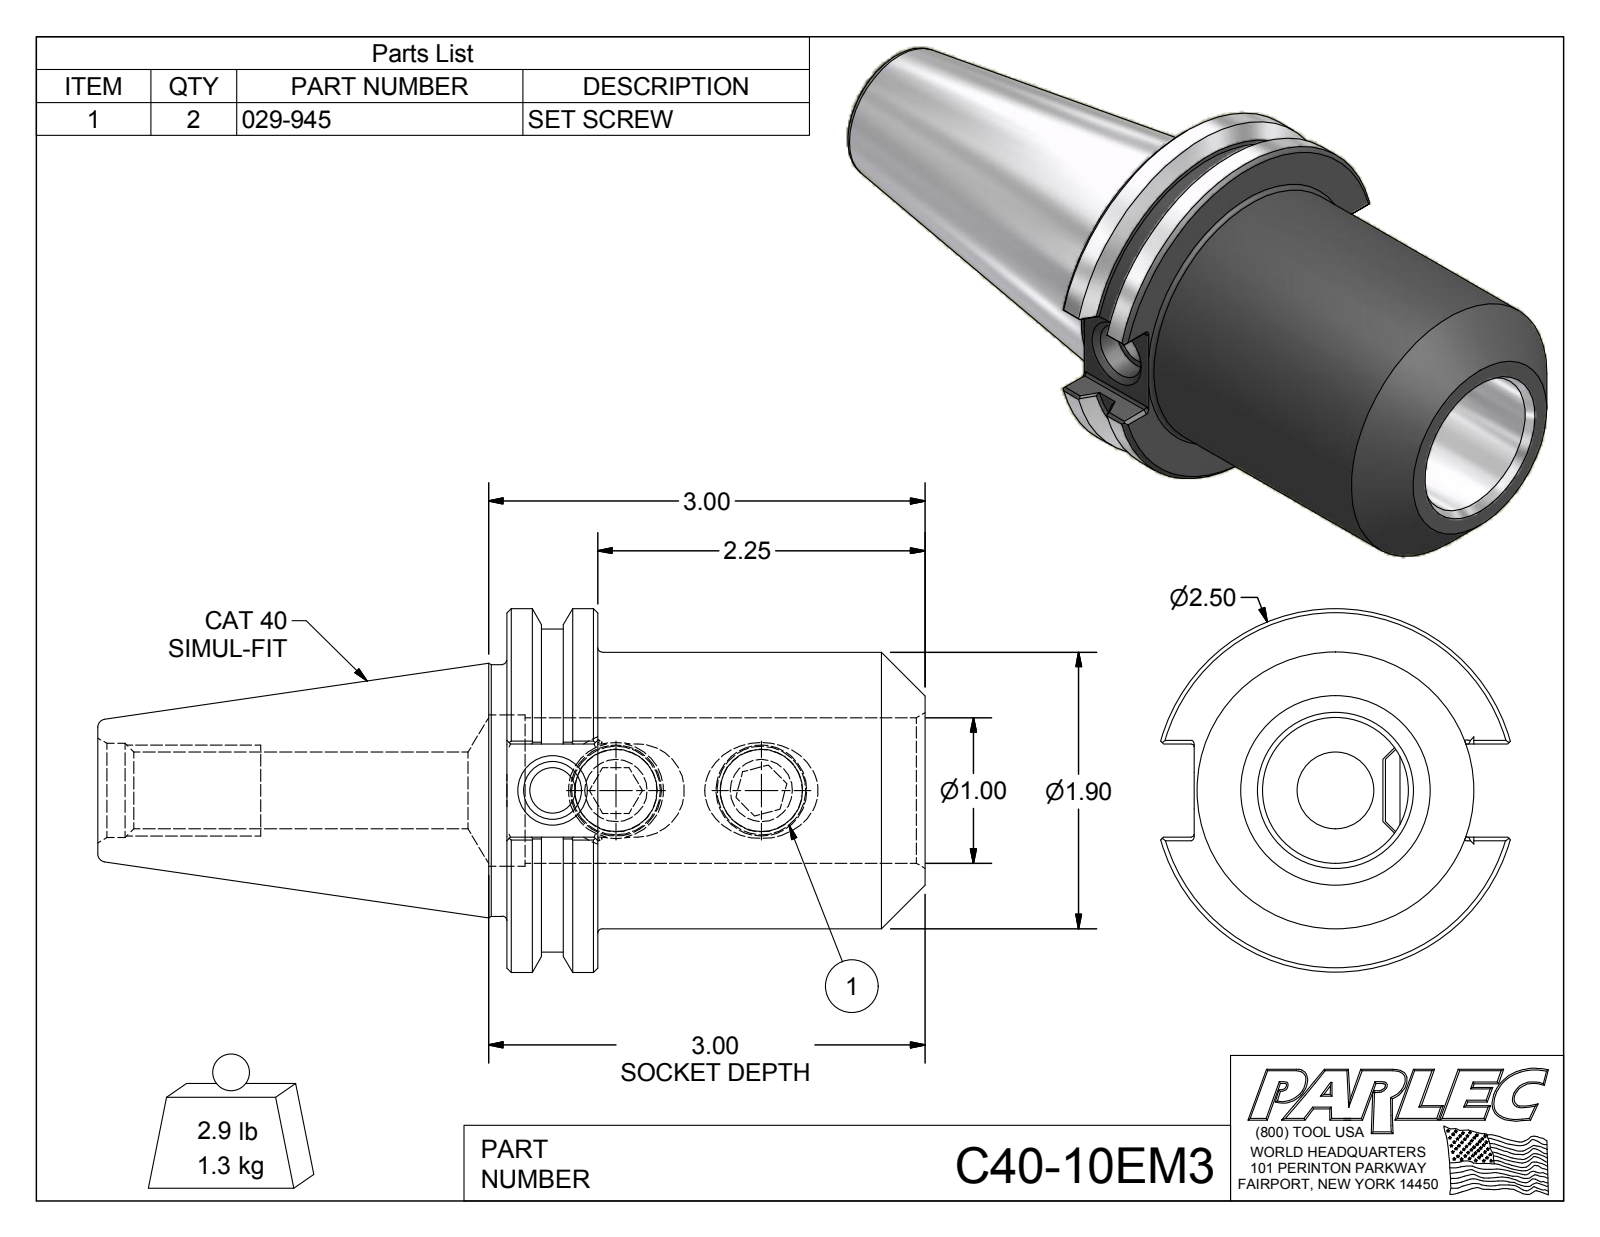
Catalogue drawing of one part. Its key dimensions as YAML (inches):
part_name: "C40-10EM3; C40-10EM3-1; 029-945"
step_written_by: "Autodesk Inventor 2012 (AUTOMOTIVE_DESIGN)"
units: inches
bodies: {solids: 3, faces: 134, planar: 65, cylindrical: 33, other: 36}
overall_size: [5.687, 2.5, 2.406]
volume: 10.01
surface_area: 55.68
round_holes:
  - {diameter: 0.565, count: 2}
  - {diameter: 0.315, count: 1}
  - {diameter: 0.399, count: 1}
  - {diameter: 0.527, count: 1}
  - {diameter: 0.648, count: 1}
  - {diameter: 1, count: 1}
  - {diameter: 1.04, count: 1}
round_bosses_or_shafts:
  - {diameter: 0.625, count: 2}
  - {diameter: 2.5, count: 1}
  - {diameter: 2.219, count: 1}
  - {diameter: 1.9, count: 1}
  - {diameter: 1.73, count: 1}
partial_cylinders:
  - {radius: 0.02, count: 12}
  - {radius: 0.32, count: 1}
face_to_face_distances: [0.625, 0.018, 2.875, 2.25, 0.5, 0.315, 0.64, 0.045, 0.063, 1.86]
hole_center_spacings: [0.435, 1, 1.435]
